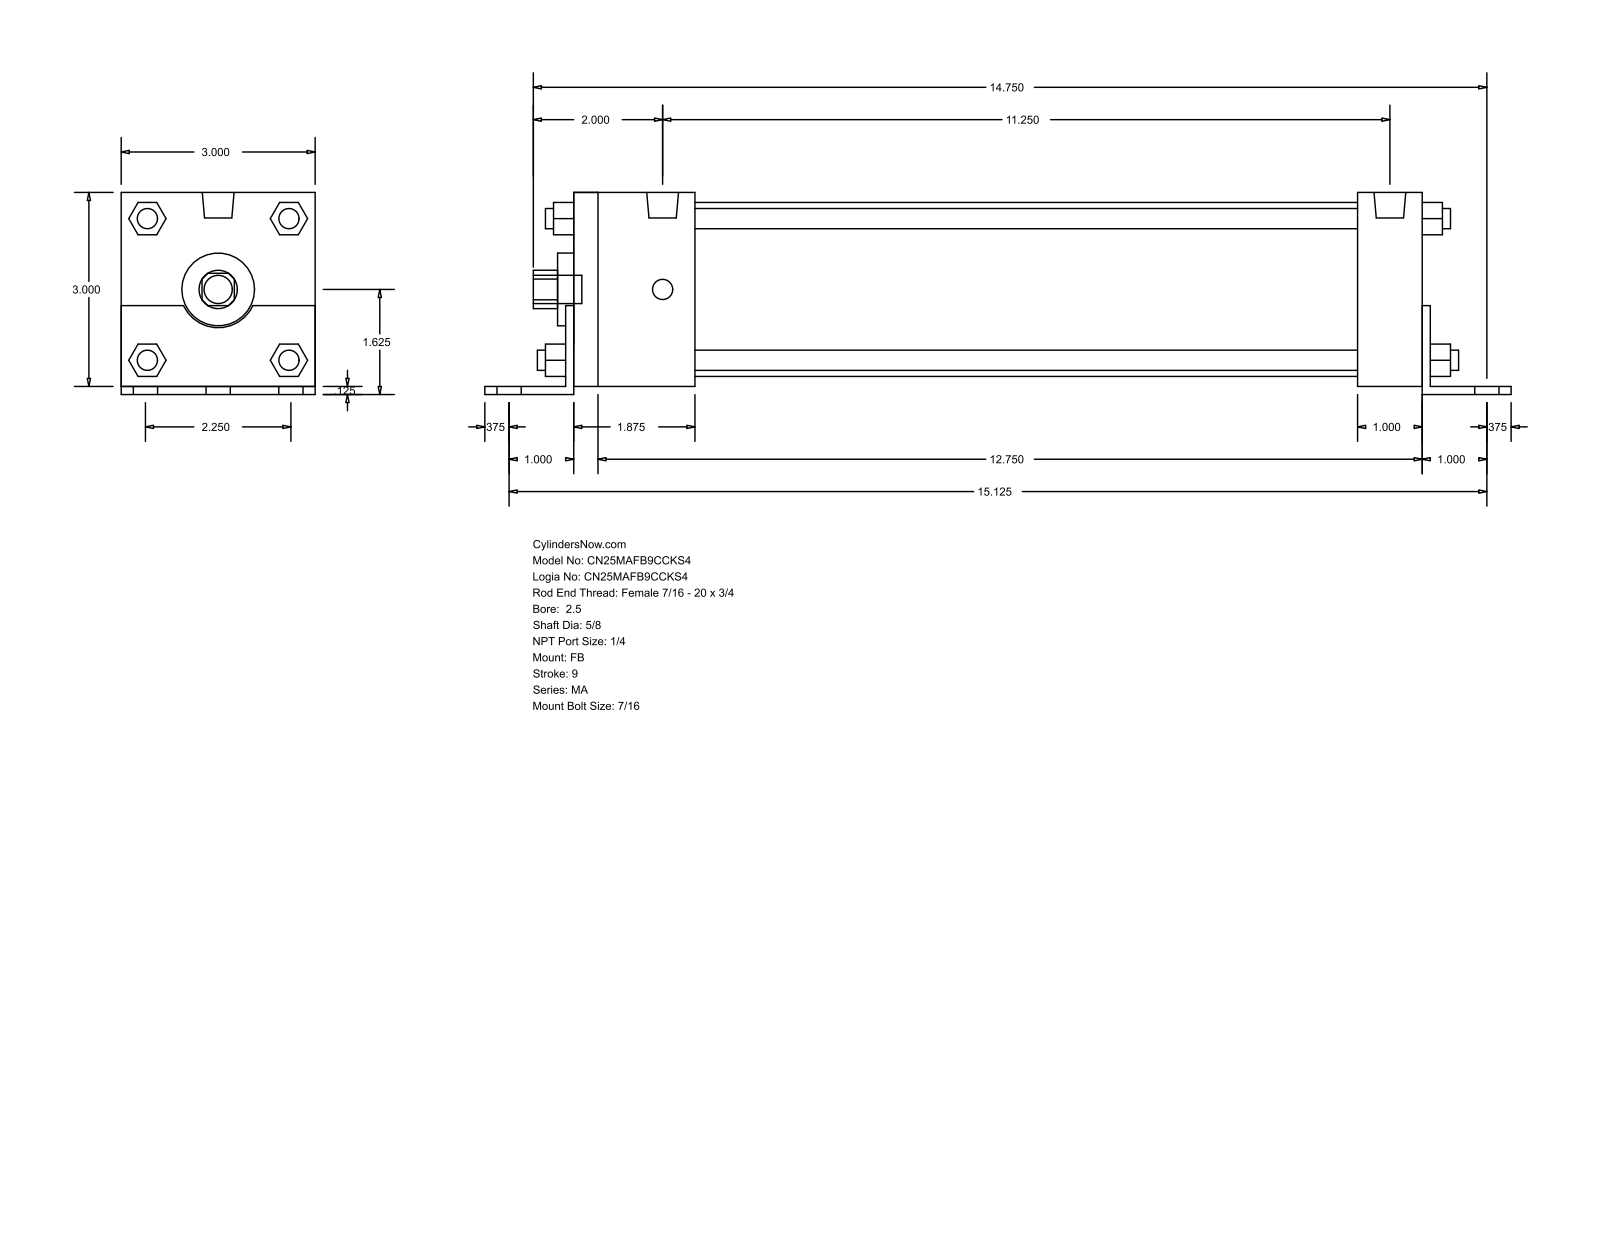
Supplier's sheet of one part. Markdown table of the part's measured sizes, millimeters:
| quantity | value |
| --- | --- |
| part name | MA_FB__0250_0.625 |
| STEP written by | GSSL Pune (CONFIG_CONTROL_DESIGN) |
| units | millimeters |
| bodies | 0 solids, 140 faces (105 planar, 35 cylindrical, 0 other) |
| overall size | 403.23 × 79.38 × 76.2 |
| round holes (diameter × count) | 15.88 × 1, 28.57 × 1, 68.33 × 1 |
| round bosses / shafts (diameter × count) | 7.94 × 8, 11.11 × 7, 12.49 × 2 |
| partial cylindrical surfaces (radius × count) | 7.54 × 1, 15.05 × 1 |
| main face-to-face distances | 76.2, 3.17, 79.37, 3.18, 336.55, 333.37, 28.58, 47.62, 25.4, 339.73 |
